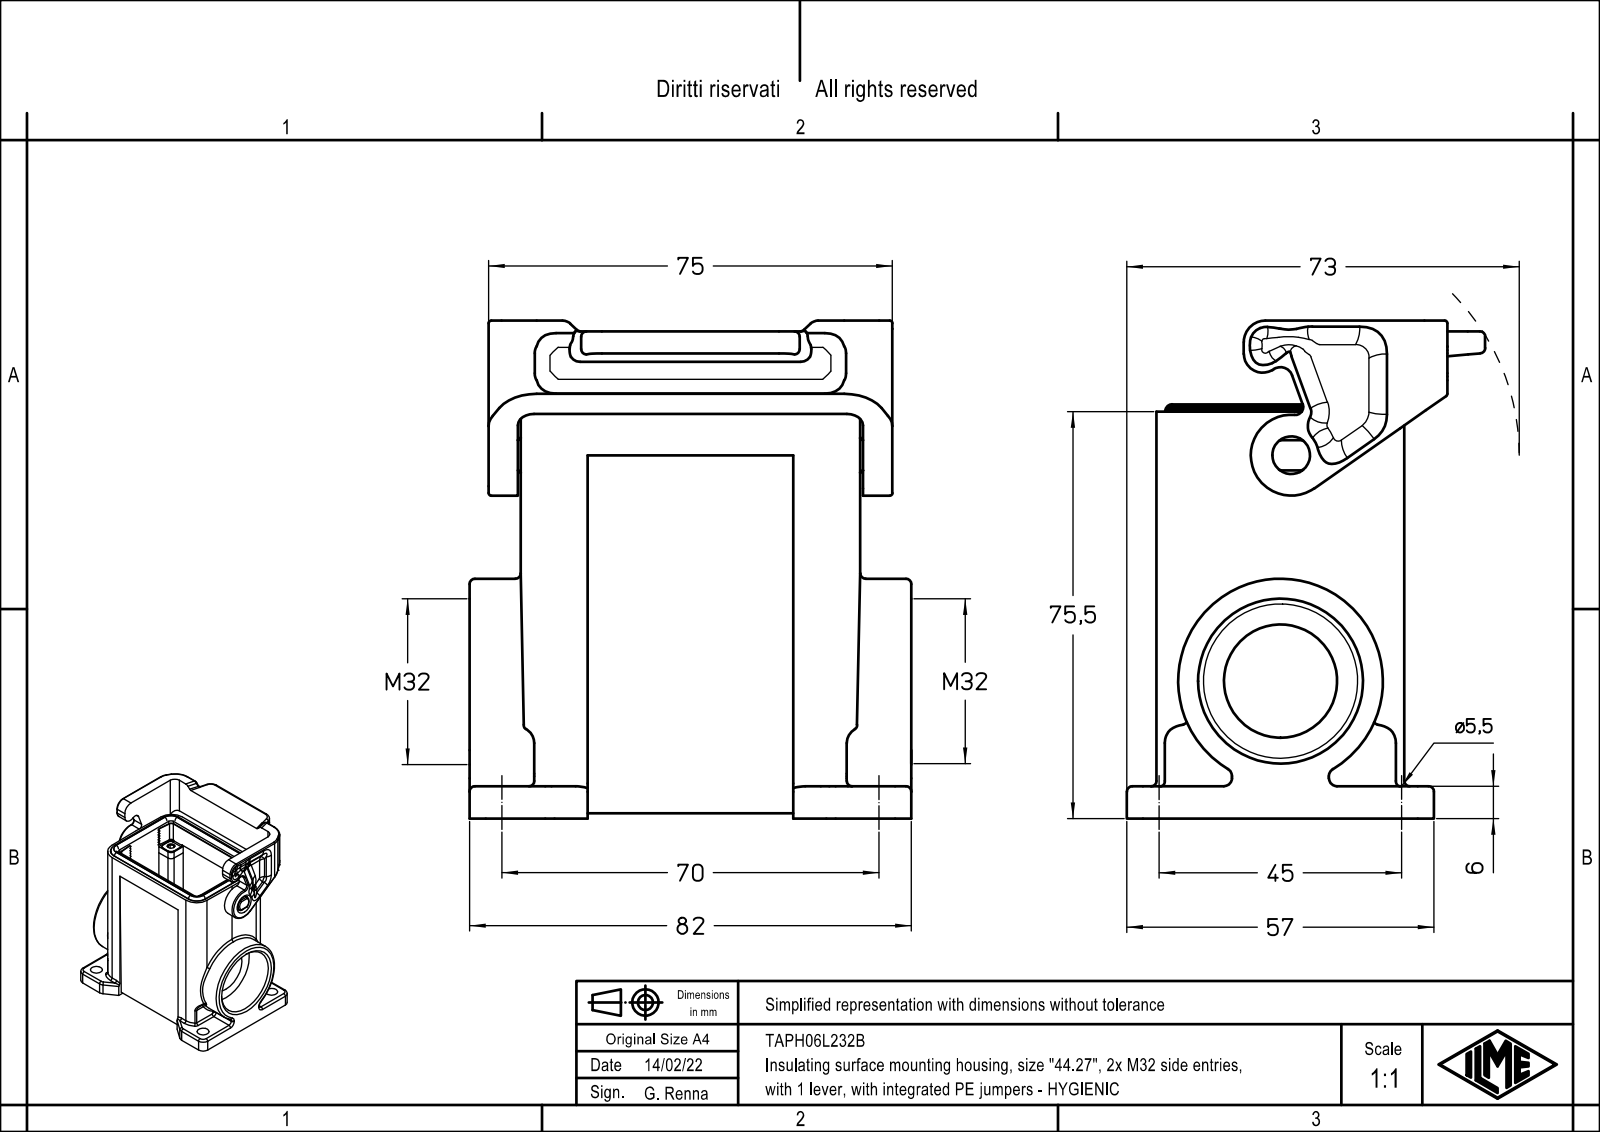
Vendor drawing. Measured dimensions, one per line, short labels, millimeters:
name: TAPH 06 L232
written by: Creo Elements/Direct Modeling 20.1B 02-Apr-2019 (C) Parametric Technology GmbH (AUTOMOTIVE_DESIGN)
unit: mm
bodies: 1 solid, 517 faces (313 planar, 168 cylindrical, 36 other)
size: 92.4 × 82 × 66.5
volume: 124 515 mm³; area: 49 413 mm²
holes: 4× ⌀3.5, 4× ⌀5.5, 1× ⌀28, 1× ⌀30.6
bosses: 1× ⌀38
rounds: 17× R1.5, 17× R3, 14× R2, 12× R1.3, 8× R1, 6× R0.5, 4× R1.6, 4× R6
face distances: 46, 5.4, 40.6, 40.59, 35.19, 5.41, 5.5, 1, 14.9, 58.1
hole spacings: 15.81, 38.28, 57.71, 67.42, 27, 44, 45, 51.62
